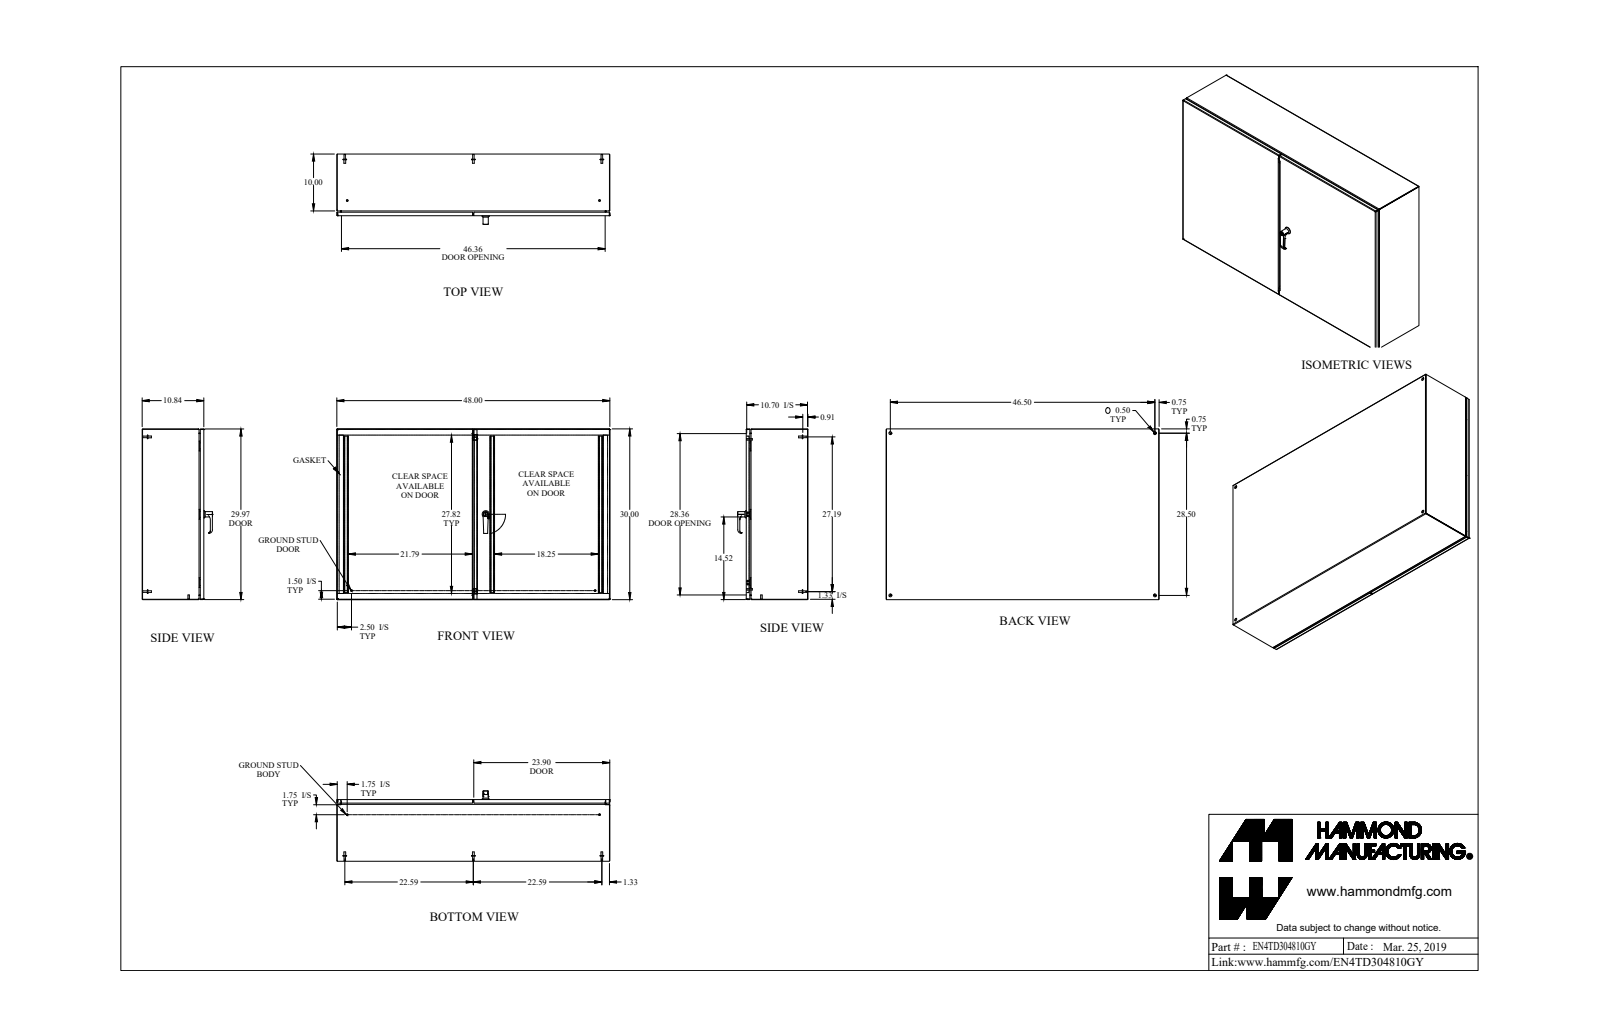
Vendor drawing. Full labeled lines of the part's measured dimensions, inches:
Part name (STEP PRODUCT): EN4TD304810GY
STEP written by: SolidWorks 2018 (AUTOMOTIVE_DESIGN)
Units: inches
Bodies: 85 solids, 2139 faces (955 planar, 790 cylindrical, 394 other)
Overall size (bounding box): 48 × 30 × 12.372
Volume: 398.8 in³ · Surface area: 10 468 in²
Round holes (diameter × count): ⌀0.196 ×5, ⌀0.176 ×4, ⌀0.265 ×4, ⌀0.5 ×4, ⌀0.24 ×3, ⌀0.242 ×3, ⌀0.172 ×2, ⌀0.25 ×2, ⌀0.256 ×2, ⌀0.26 ×2, ⌀0.313 ×2, ⌀0.394 ×2
Round bosses / shafts (diameter × count): ⌀0.25 ×12, ⌀0.313 ×8, ⌀0.625 ×6, ⌀0.27 ×6, ⌀0.51 ×4, ⌀0.281 ×4, ⌀0.156 ×4, ⌀0.75 ×3
Partial cylindrical surfaces — rounded edges, fillets, slot ends (radius × count): R0.036 ×26, R0.108 ×26, R0.063 ×25, R0.094 ×20, R0.043 ×18, R0.081 ×18, R0.02 ×16, R0.016 ×15
Main face-to-face distances: 0.072, 10.77, 10.698, 10.842, 29.928, 47.928, 29.856, 30, 47.856, 48
Hole centre spacings: 0.786, 13.188, 20.798, 25.447, 25.752, 28.5, 29.139, 46.5
